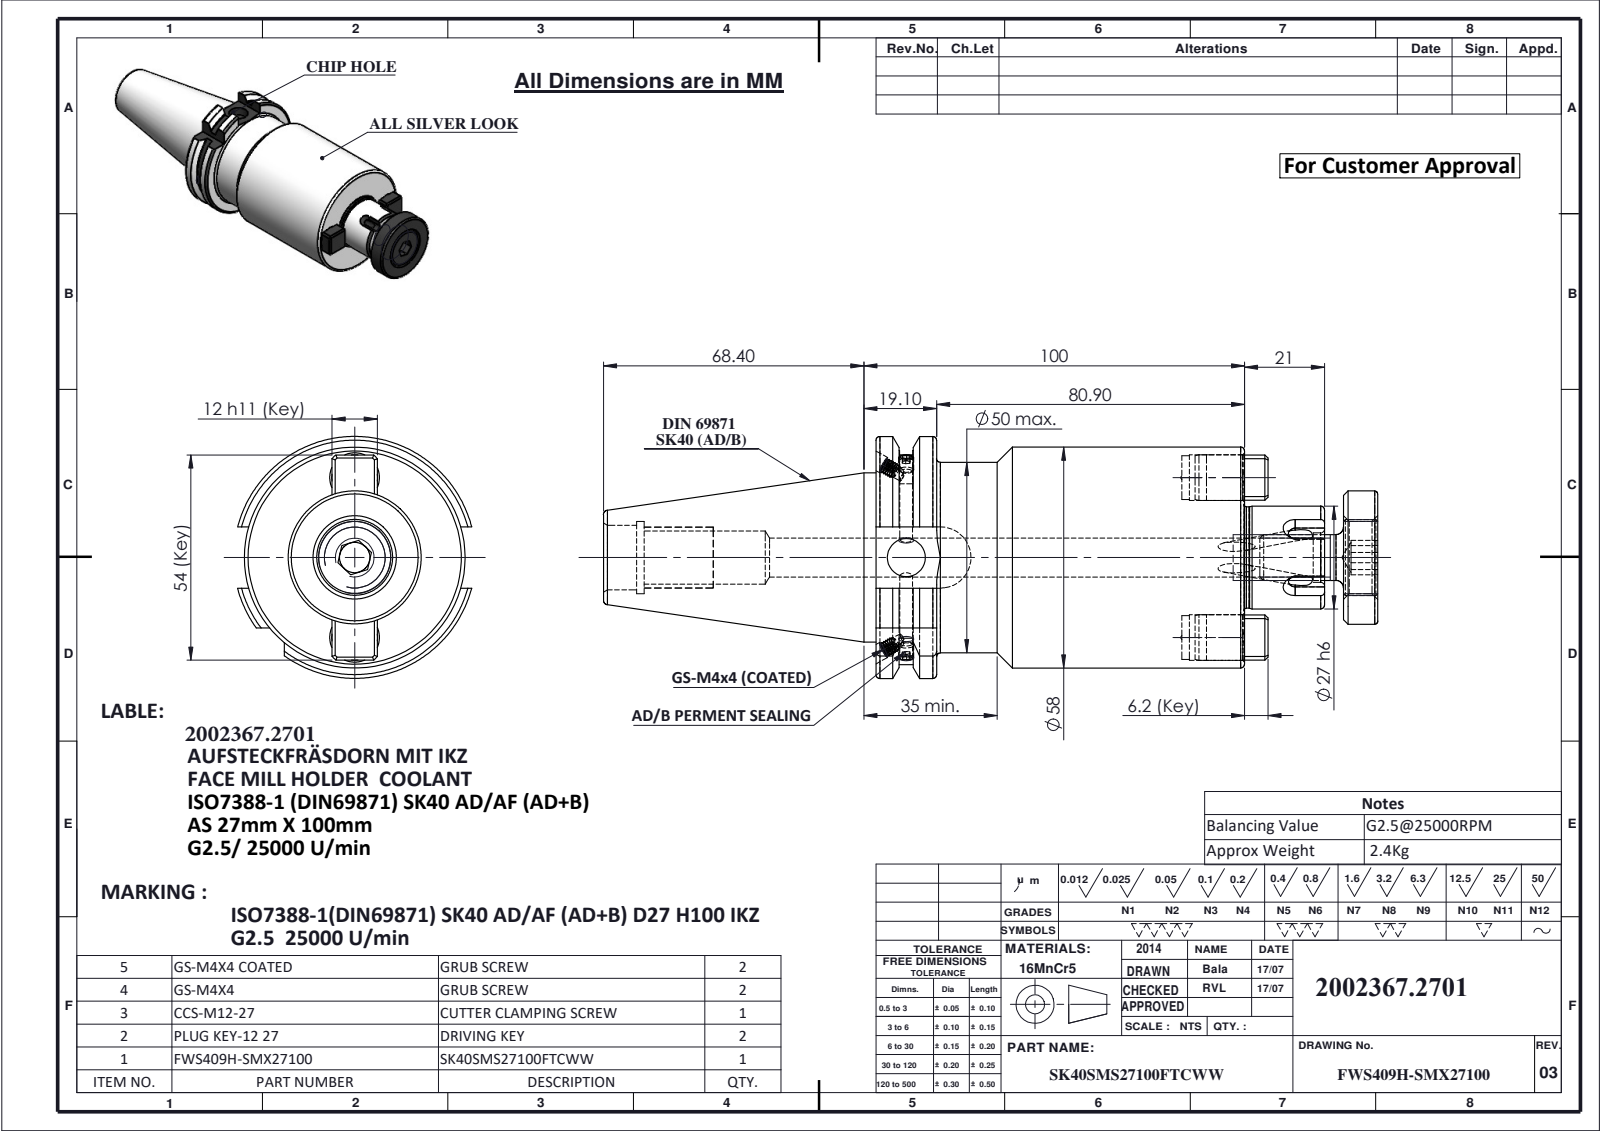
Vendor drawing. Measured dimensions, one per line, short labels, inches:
name: CCS-M12-27; SK40SMS27100FWW; GS-M4X4-COATING_DIN 913 - M4 x 4-N; CCS-M12-27-1 (+4 more)
written by: SolidWorks 2024 (CONFIG_CONTROL_DESIGN)
unit: in
bodies: 9 solids, 421 faces (132 planar, 120 cylindrical, 169 other)
size: 8.008 × 2.502 × 2.42
volume: 19.35 in³; area: 77.65 in²
holes: 4× ⌀0.118, 3× ⌀0.13, 2× ⌀0.177, 2× ⌀0.453, 2× ⌀0.472, 1× ⌀0.394, 1× ⌀0.402, 1× ⌀0.512, 1× ⌀0.551, 1× ⌀0.669, 1× ⌀0.748
bosses: 4× ⌀0.157, 2× ⌀0.473, 2× ⌀0.473, 1× ⌀2.283, 1× ⌀1.969, 1× ⌀1.75, 1× ⌀1.378, 1× ⌀1.063
rounds: 4× R0.079, 2× R0.305, 1× R0.317, 1× R1.107, 1× R1.251
face distances: 3.811, 1.378, 5.189, 0.626, 3.185, 4.563, 4.835, 4.209, 1.024, 0.354
hole spacings: 0.827, 1.654
